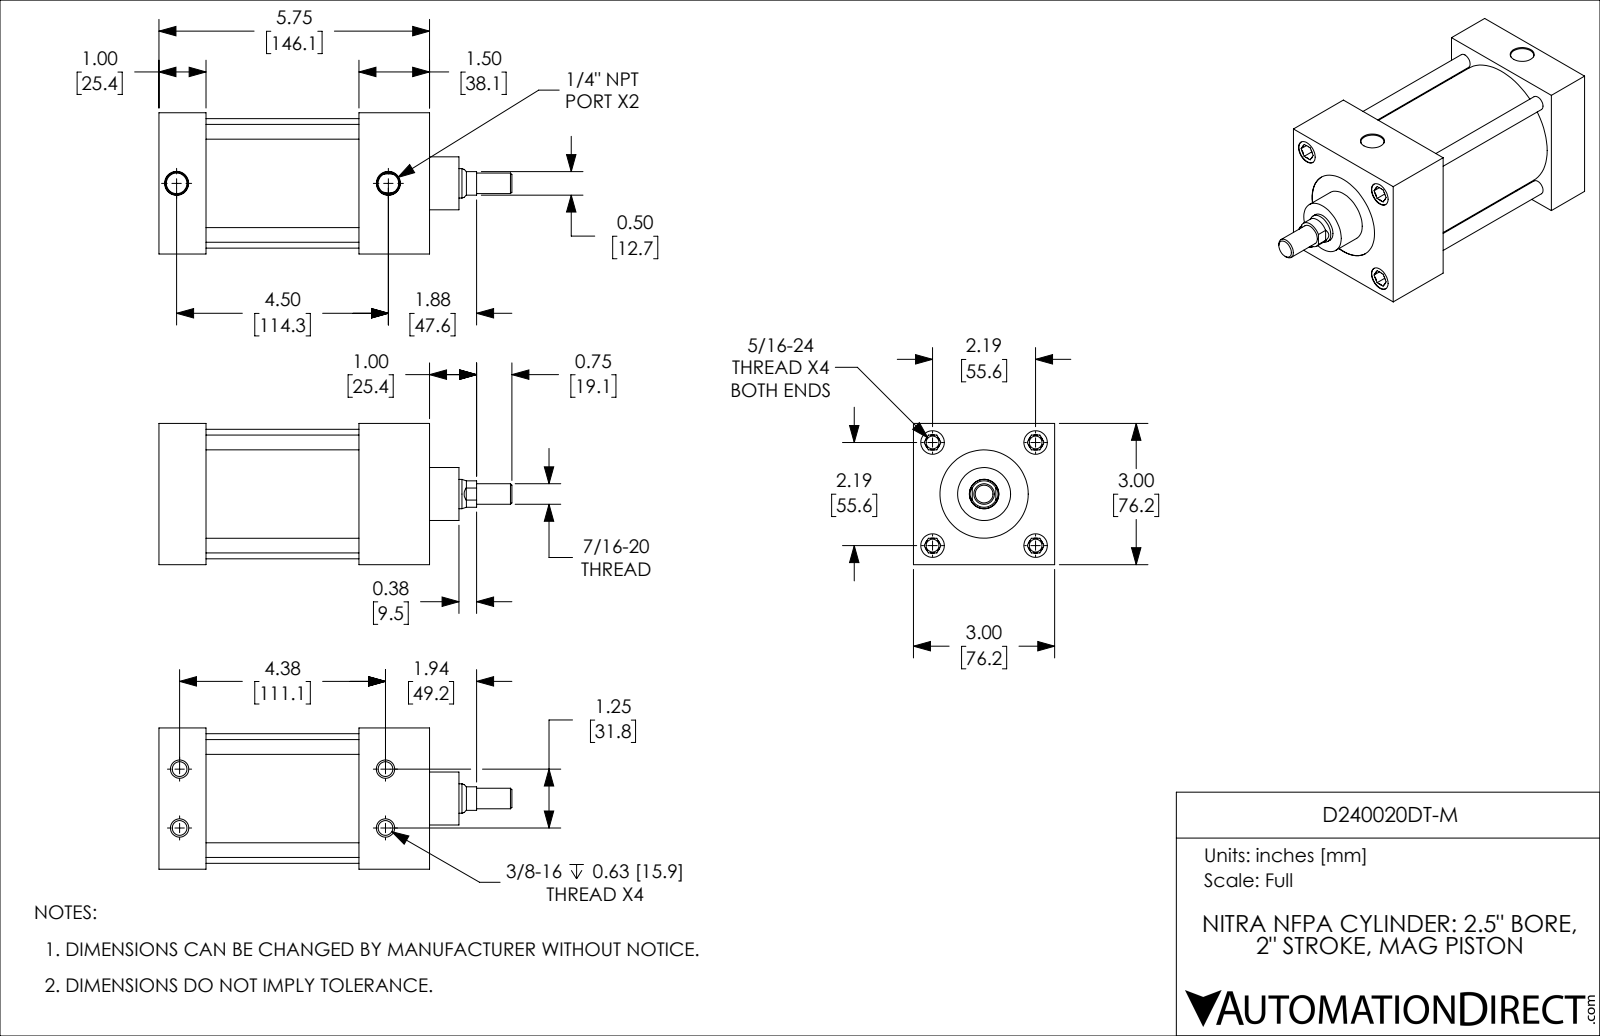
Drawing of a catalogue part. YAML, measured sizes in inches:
part_name: "D240020DT-M_PISTON_KK1; D240020DT-M_BODY; D240020DT-M"
step_written_by: "SolidWorks 2019 (CONFIG_CONTROL_DESIGN)"
units: inches
bodies: {solids: 2, faces: 200, planar: 58, cylindrical: 62, other: 80}
overall_size: [7.5, 3, 3]
volume: 33.32
surface_area: 176.9
round_holes:
  - {diameter: 0.272, count: 4}
  - {diameter: 0.313, count: 4}
  - {diameter: 0.5, count: 4}
  - {diameter: 0.438, count: 2}
  - {diameter: 0.626, count: 1}
  - {diameter: 1.875, count: 1}
  - {diameter: 2.501, count: 1}
round_bosses_or_shafts:
  - {diameter: 0.312, count: 4}
  - {diameter: 2.751, count: 1}
  - {diameter: 2.499, count: 1}
  - {diameter: 1.125, count: 1}
  - {diameter: 0.624, count: 1}
  - {diameter: 0.437, count: 1}
partial_cylinders:
  - {radius: 0.281, count: 1}
face_to_face_distances: [3, 1, 3.25, 4.25, 5.75, 4.75, 1.5, 1.25, 2.25, 2]
hole_center_spacings: [1.548, 2.19, 4.481, 0.628, 0.628, 1.25, 3.097, 4.375]
